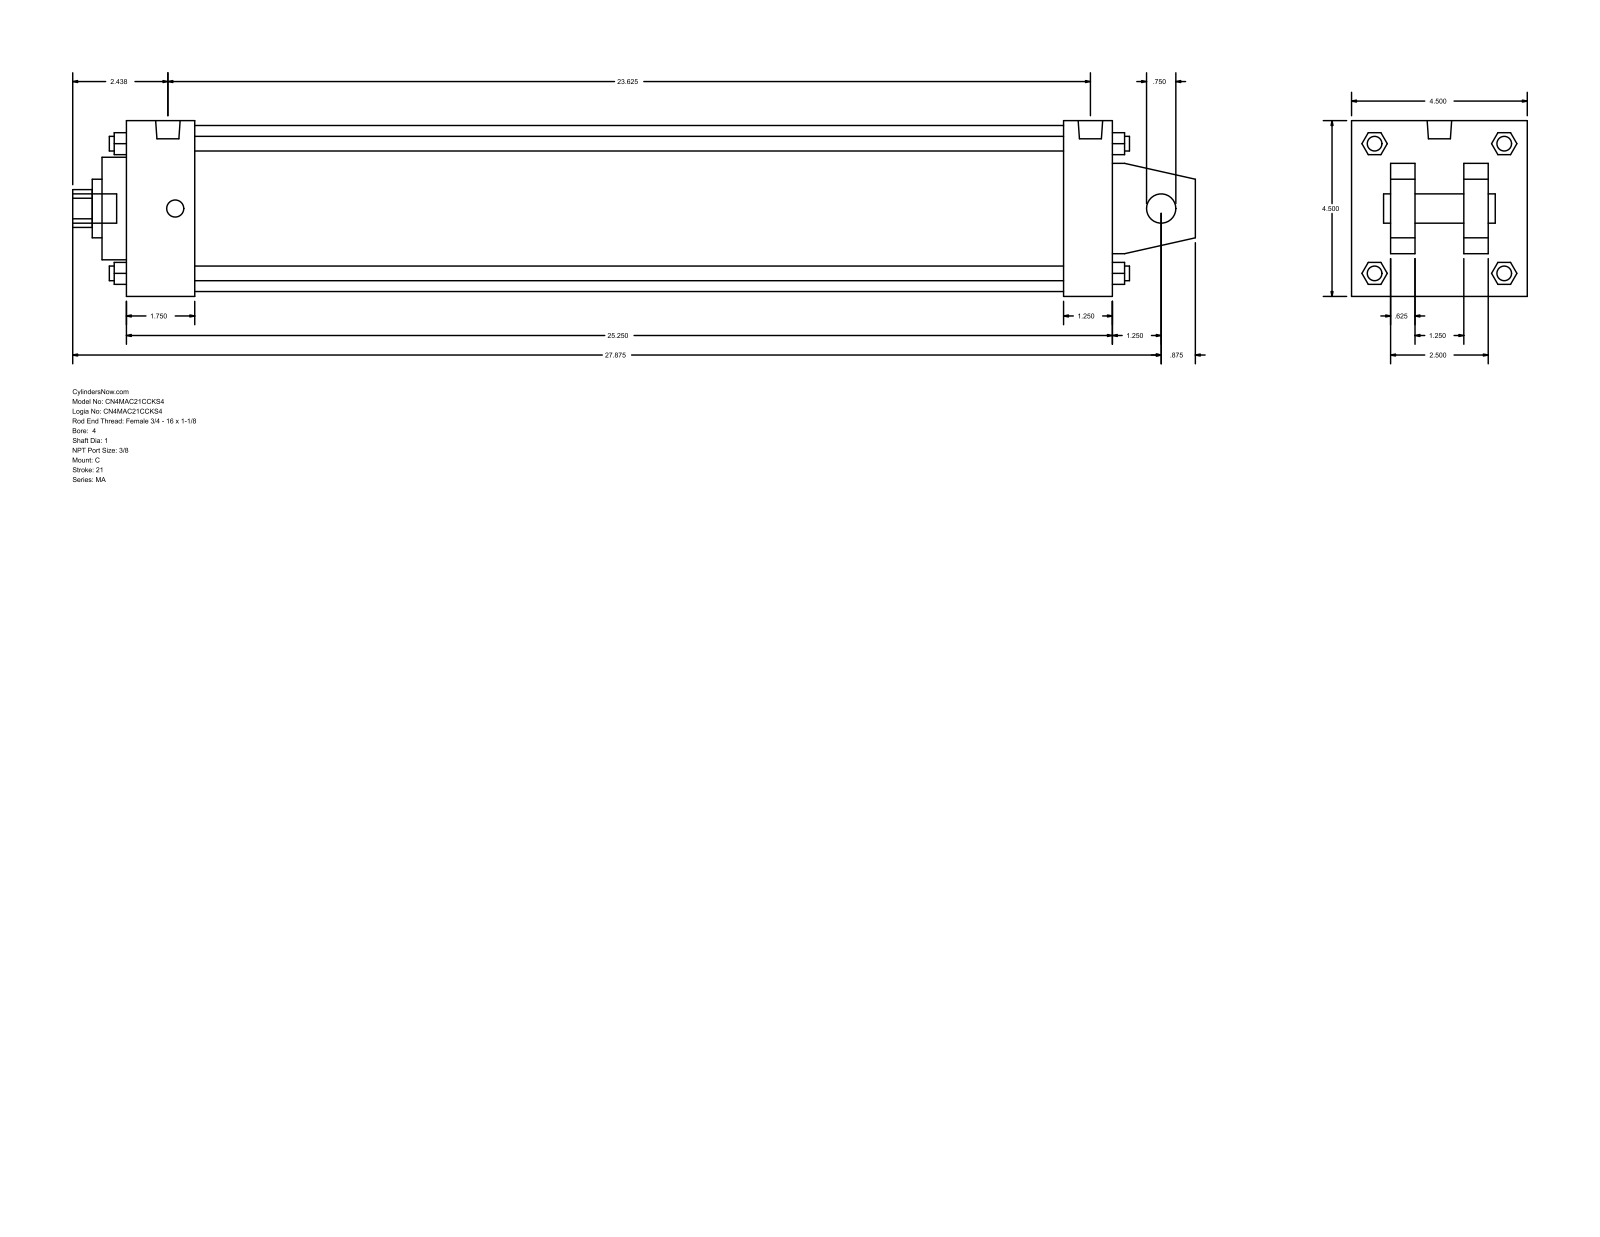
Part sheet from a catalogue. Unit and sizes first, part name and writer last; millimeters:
Units: millimetres
Overall size (bounding box): 730.25 × 114.3 × 114.3
Round holes (diameter × count): ⌀19.05 ×1, ⌀25.4 ×1, ⌀38.1 ×1, ⌀66.67 ×1, ⌀107.95 ×1
Round bosses / shafts (diameter × count): ⌀11.11 ×4, ⌀9.53 ×4, ⌀15.93 ×2, ⌀19.05 ×1
Partial cylindrical surfaces — rounded edges, fillets, slot ends (radius × count): R12.29 ×1
Main face-to-face distances: 114.3, 641.35, 15.87, 73.03, 41.27, 25.4, 88.9, 47.63, 609.6, 31.75
Bodies: 0 solids, 141 faces (109 planar, 32 cylindrical, 0 other)
Part name (STEP PRODUCT): MA_C__0400_1
STEP written by: GSSL Pune (CONFIG_CONTROL_DESIGN)
